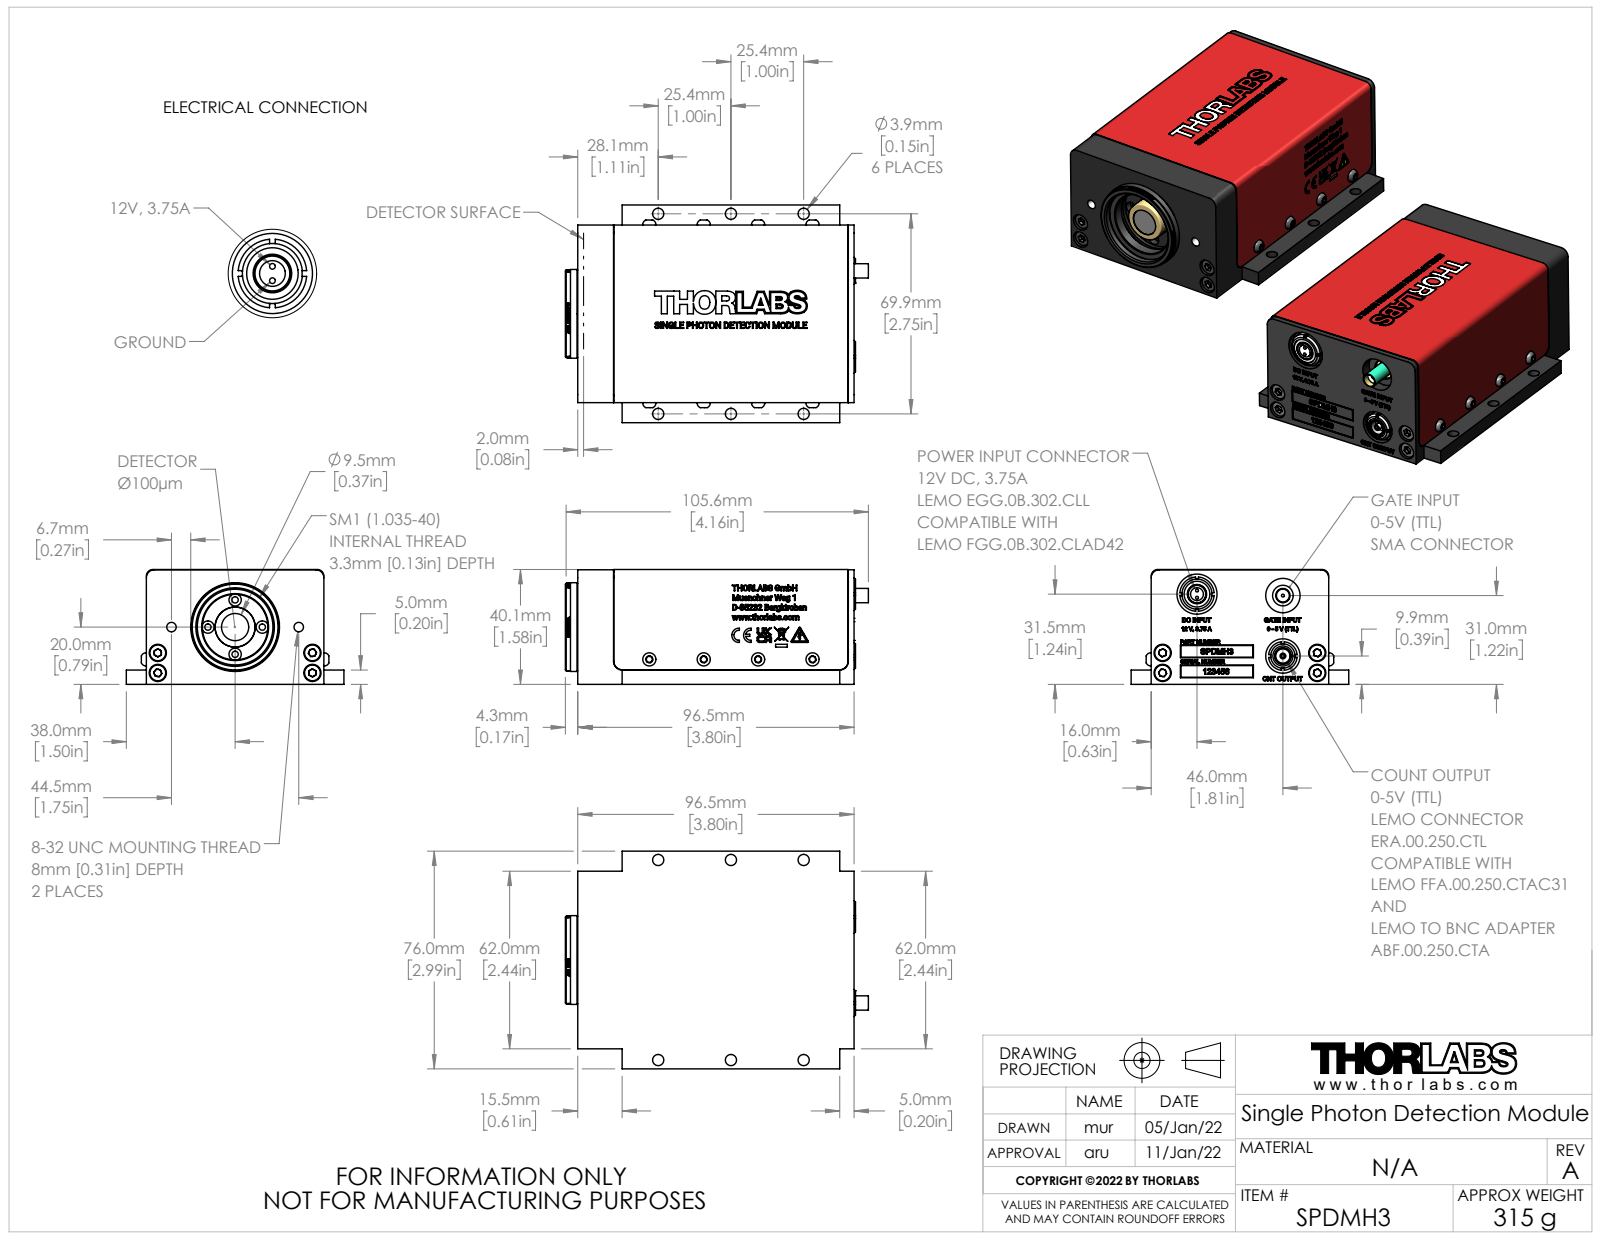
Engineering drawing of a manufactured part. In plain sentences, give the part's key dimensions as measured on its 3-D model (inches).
The part is named "22.04.06_SPDMH3 WEB". Its 3-D file was written by "SolidWorks 2019 (AUTOMOTIVE_DESIGN)". It is 0 solids with 3327 faces: 2411 planar, 260 cylindrical and 656 other. Overall it measures 4.166 by 2.992 by 1.579 inches. Round holes: 6 of diameter 0.154, 4 of diameter 0.039, 4 of diameter 0.079, 4 of diameter 0.087, 4 of diameter 0.097, 4 of diameter 0.126, 4 of diameter 0.169, 4 of diameter 0.236, 2 of diameter 0.078, 2 of diameter 0.079, 2 of diameter 0.13, 2 of diameter 0.283. Round bosses or shafts: 4 of diameter 0.217, 4 of diameter 0.118, 1 of diameter 1.22, 1 of diameter 1.2, 1 of diameter 1.196, 1 of diameter 1, 1 of diameter 0.98, 1 of diameter 0.55. Partial cylindrical surfaces (rounded edges, fillets, slot ends): 6 of radius 0.008, 6 of radius 0.029, 4 of radius 0.049, 4 of radius 0.055, 4 of radius 0.118, 3 of radius 0.006, 3 of radius 0.012, 3 of radius 0.033. The main face-to-face distances are 0.031, 0.197, 1.547, 1.35, 1.579, 1.382, 2.441, 2.409, 2.992, 0.61. The hole center spacings are 0.748, 1, 0.374, 0.529, 0.952, 0.965, 1.15, 1.811.
